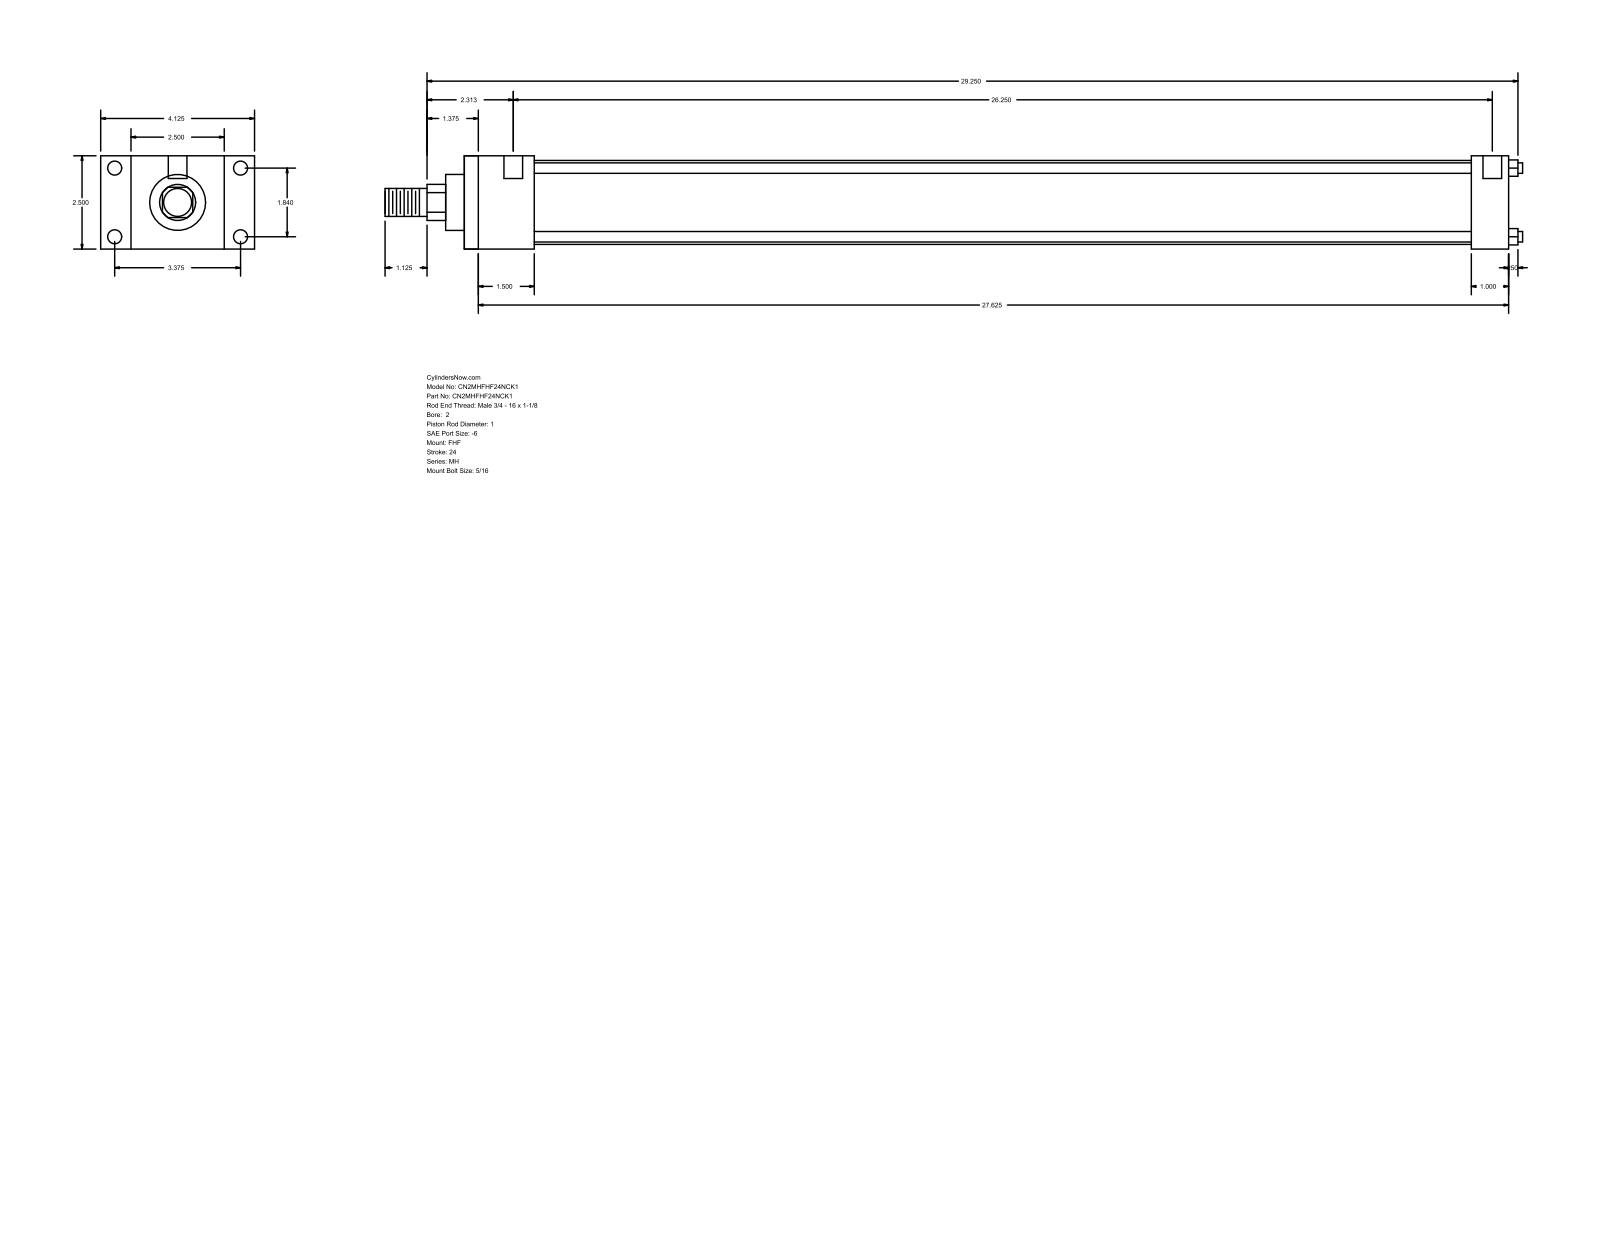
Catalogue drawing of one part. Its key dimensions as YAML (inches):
part_name: "MH_FHF__0200_1"
step_written_by: "GSSL Pune (CONFIG_CONTROL_DESIGN)"
units: inches
bodies: {solids: 0, faces: 88, planar: 60, cylindrical: 28, other: 0}
overall_size: [30.5, 4.125, 2.5]
round_holes:
  - {diameter: 0.219, count: 4}
  - {diameter: 0.375, count: 4}
  - {diameter: 0.5, count: 2}
round_bosses_or_shafts:
  - {diameter: 0.281, count: 4}
  - {diameter: 2.25, count: 1}
  - {diameter: 1.5, count: 1}
  - {diameter: 1, count: 1}
  - {diameter: 0.75, count: 1}
partial_cylinders:
  - {radius: 0.484, count: 1}
face_to_face_distances: [2.5, 28, 1.875, 26.125, 0.813, 3.313, 4.125, 1, 27, 25.125]
hole_center_spacings: [1.84, 3.375, 3.844, 26.562, 0.125, 0.187, 26.25, 26.375]
